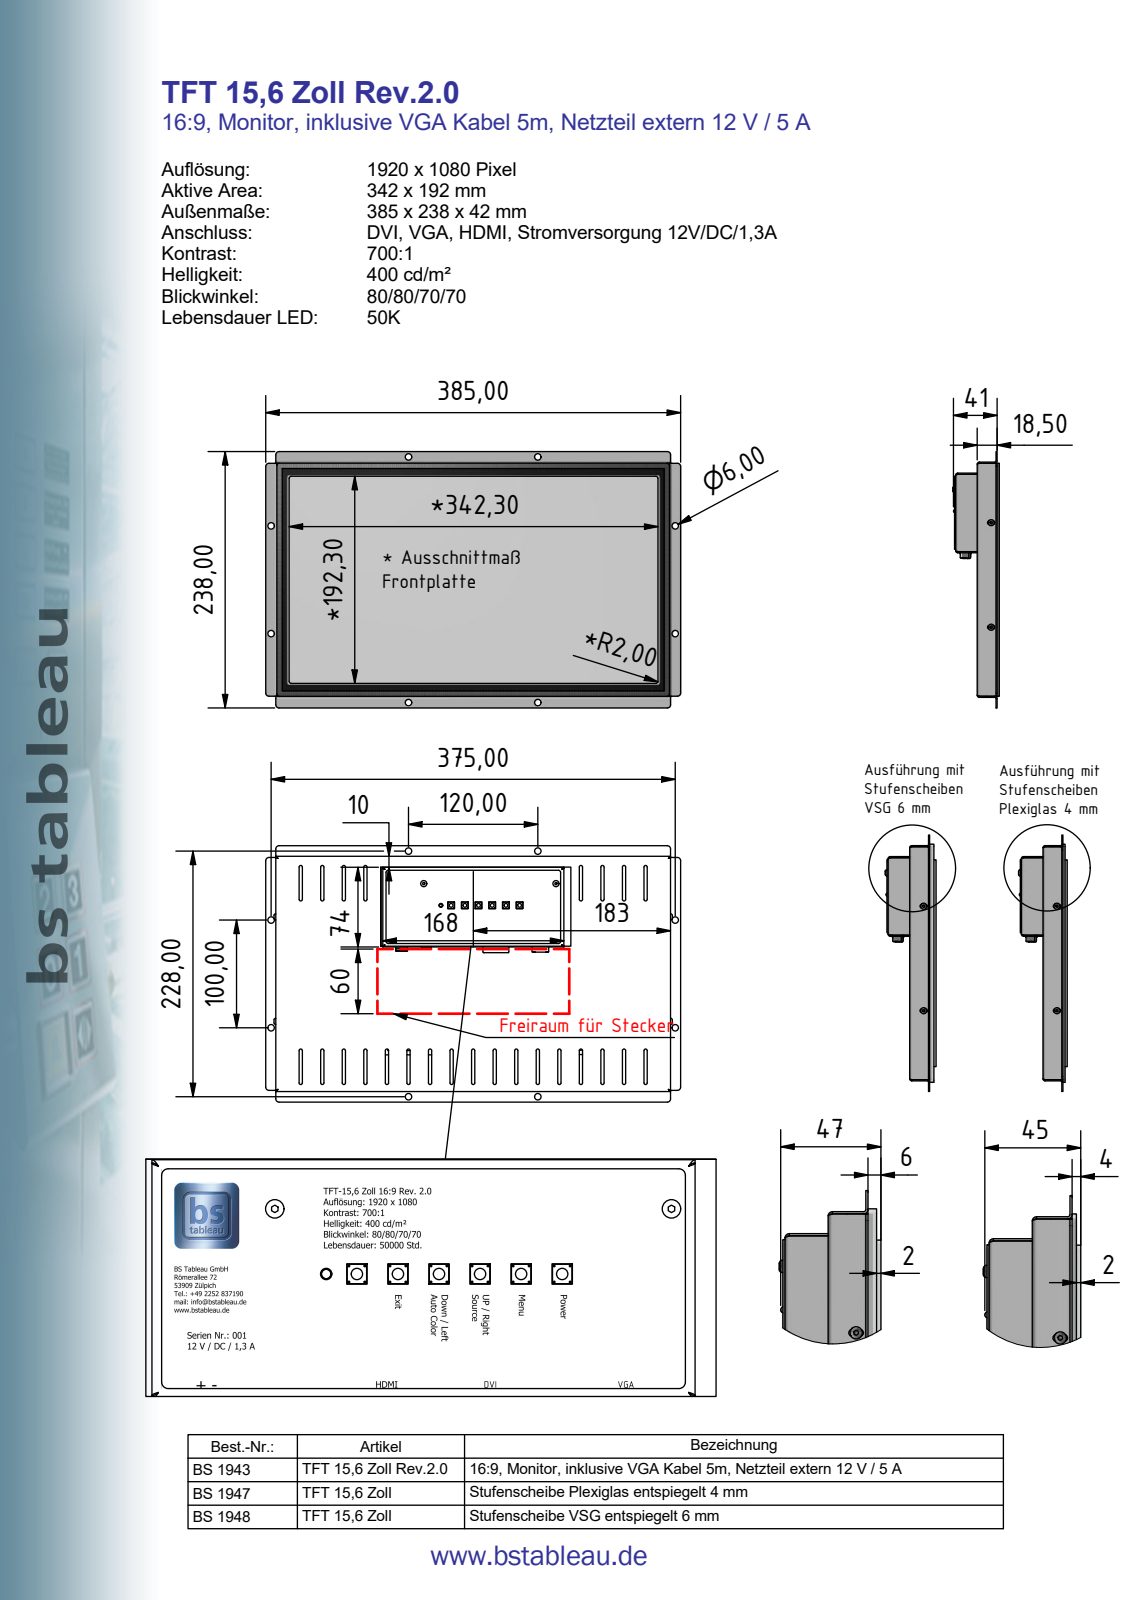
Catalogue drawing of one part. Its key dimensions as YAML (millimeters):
part_name: "20000024 TFT 15,6 Zoll 16_9 Rev.2.0; 00000010 NB-4pol; 00003372 THV65-G156HTN02 V0 - MSC; 00000078 OSD-Board THV 65 - MSC (+8 more)"
step_written_by: "Autodesk Inventor 2019 (AUTOMOTIVE_DESIGN)"
units: millimeters
bodies: {solids: 35, faces: 4694, planar: 3182, cylindrical: 1083, other: 429}
overall_size: [385, 238, 43.15]
volume: 926513
surface_area: 454171
round_holes:
  - {diameter: 1, count: 15}
  - {diameter: 2.46, count: 10}
  - {diameter: 6, count: 9}
  - {diameter: 5.41, count: 8}
  - {diameter: 3.2, count: 6}
  - {diameter: 3.4, count: 4}
  - {diameter: 1.27, count: 2}
  - {diameter: 2.26, count: 2}
  - {diameter: 2.5, count: 2}
  - {diameter: 2.54, count: 2}
  - {diameter: 3.17, count: 2}
  - {diameter: 3.3, count: 2}
round_bosses_or_shafts:
  - {diameter: 0.5, count: 24}
  - {diameter: 3, count: 11}
  - {diameter: 5.7, count: 10}
  - {diameter: 5.42, count: 8}
  - {diameter: 3.5, count: 6}
  - {diameter: 3.56, count: 2}
  - {diameter: 1, count: 2}
  - {diameter: 2.9, count: 1}
partial_cylinders:
  - {radius: 0.1, count: 174}
  - {radius: 0.13, count: 82}
  - {radius: 0.5, count: 72}
  - {radius: 1.5, count: 64}
  - {radius: 0.25, count: 41}
  - {radius: 1, count: 20}
  - {radius: 0.51, count: 17}
  - {radius: 2, count: 16}
face_to_face_distances: [1, 9.8, 17.5, 8.7, 18.5, 7.7, 20, 37.5, 5, 15]
hole_center_spacings: [2.26, 3.95, 2.29, 4.58, 4.52, 6.02, 6.04, 6.87]
